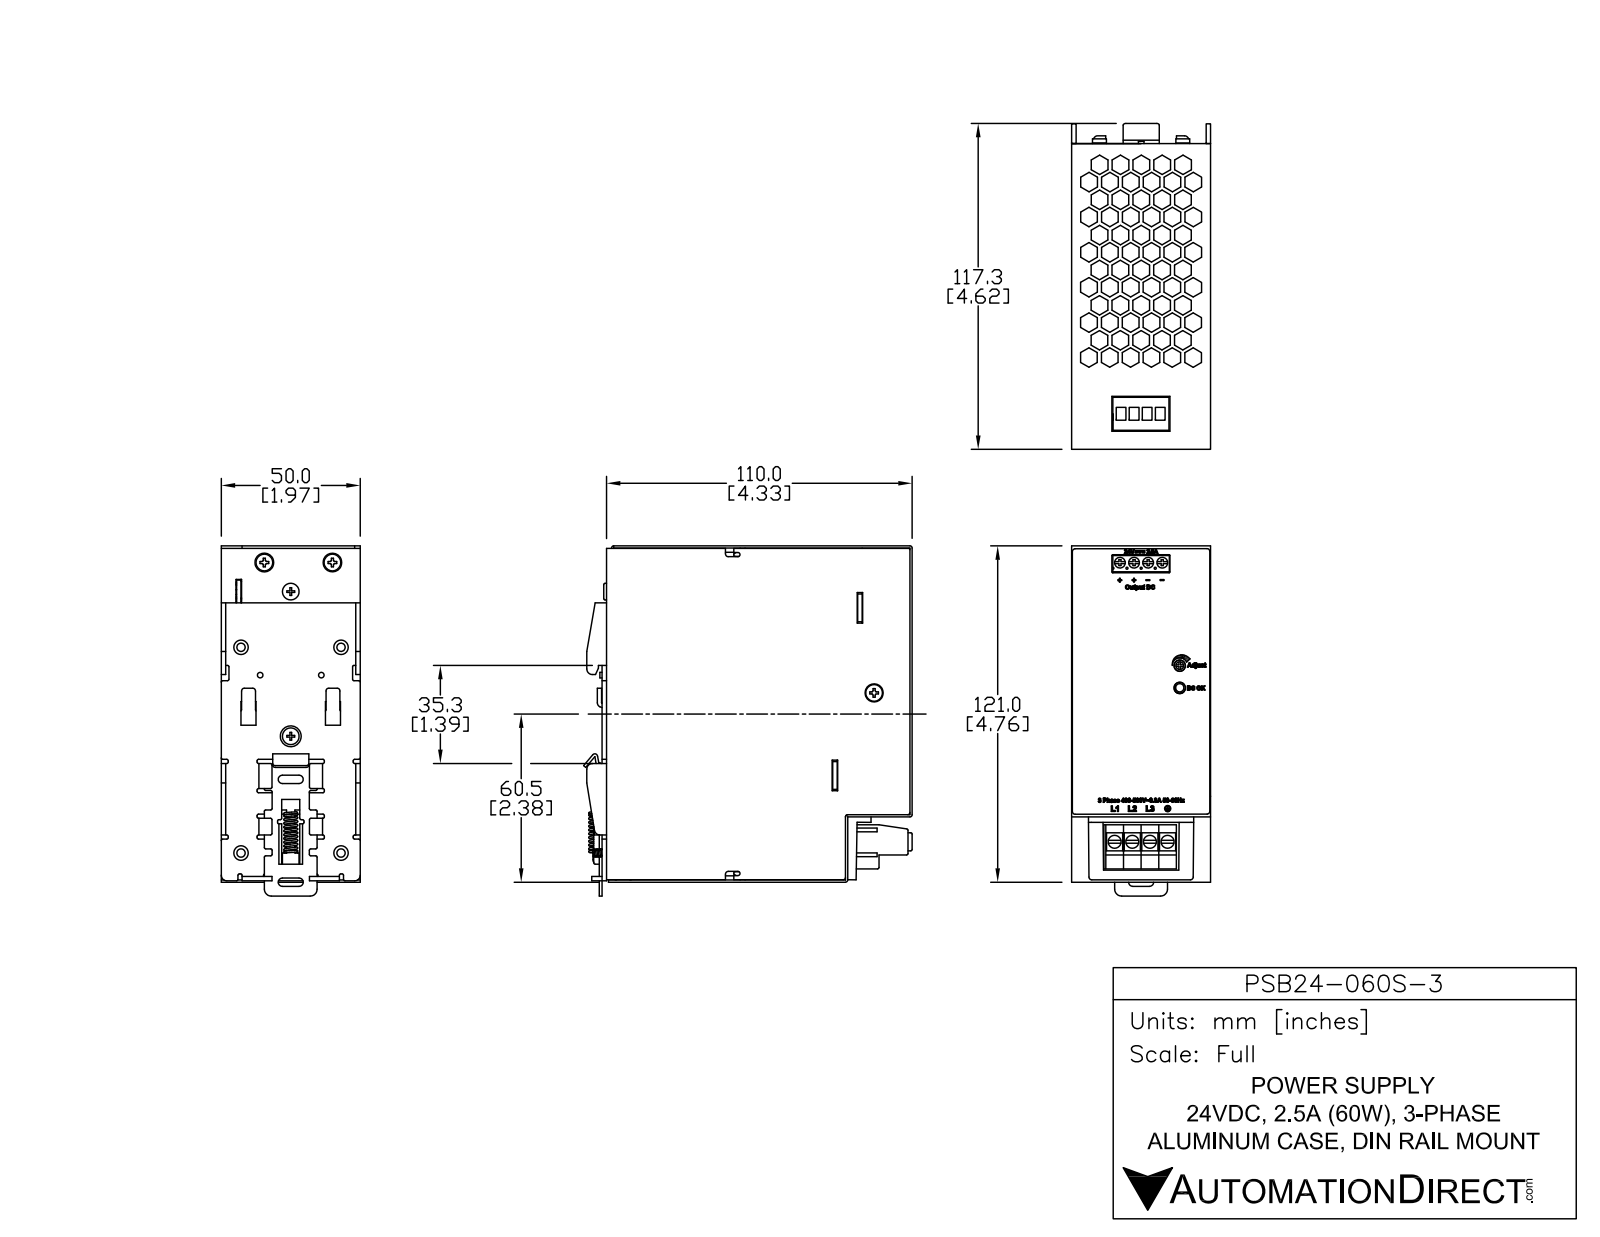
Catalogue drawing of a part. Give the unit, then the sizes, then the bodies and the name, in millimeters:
Units: millimetres
Overall size (bounding box): 126 × 118.4 × 50.1
Round holes (diameter × count): ⌀2.5 ×19, ⌀4.2 ×8, ⌀1.8 ×4, ⌀3.9 ×4, ⌀4 ×4, ⌀4 ×4, ⌀4.6 ×4, ⌀4.9 ×4, ⌀4.1 ×3, ⌀1.6 ×2, ⌀2 ×2, ⌀3.5 ×2
Round bosses / shafts (diameter × count): ⌀6 ×10, ⌀3 ×10, ⌀3.5 ×5, ⌀5.2 ×4, ⌀4.7 ×4, ⌀4 ×4, ⌀2 ×4, ⌀5 ×2
Partial cylindrical surfaces — rounded edges, fillets, slot ends (radius × count): R0.5 ×138, R0.8 ×46, R1 ×45, R0.1 ×37, R0.2 ×32, R0.9 ×26, R0.9 ×22, R0.8 ×14
Main face-to-face distances: 1.5, 48.5, 1.6, 0.4, 50, 1.9, 47, 42.9, 46.6, 48.1
Hole centre spacings: 30, 5.1, 6.4, 60.5, 62.5, 65.6, 5, 7.5
Volume: 128 100 mm³ · Surface area: 207 900 mm²
Bodies: 43 solids, 6264 faces (3858 planar, 922 cylindrical, 1484 other)
Part name (STEP PRODUCT): 2958055702_PWB; 326356700000; 347205340102-2; 2968150902_DCT-1569 (+8 more)
STEP written by: SolidWorks 2014 (AUTOMOTIVE_DESIGN)
